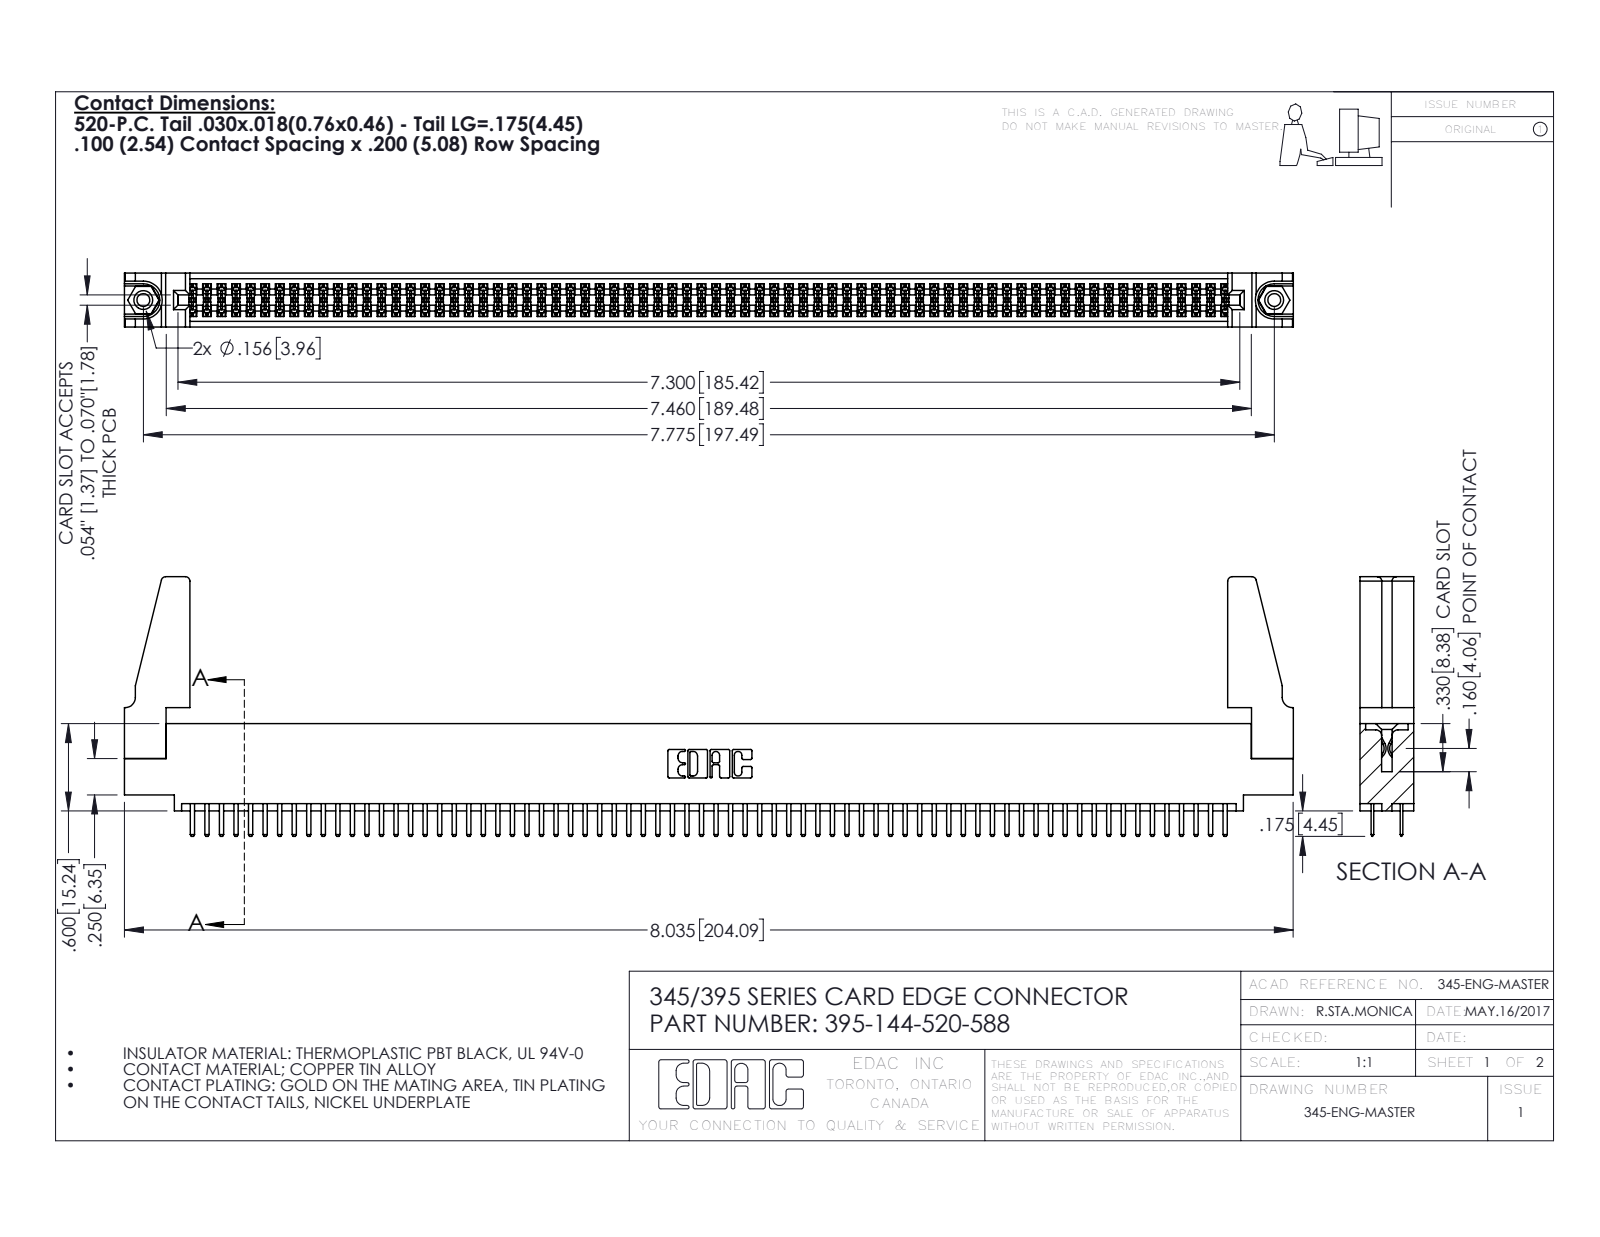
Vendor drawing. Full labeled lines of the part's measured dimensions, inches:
Part name (STEP PRODUCT): 345 Part_0.110 Offset - 0.156 Dia-TH; 345-292-001_345-293-120; 395-144-520-588; 345-250-001_345-250-001-102 (+1 more)
STEP written by: SolidWorks 2016 (CONFIG_CONTROL_DESIGN)
Units: inches
Bodies: 149 solids, 8030 faces (5196 planar, 2818 cylindrical, 16 other)
Overall size (bounding box): 8.036 × 1.785 × 0.37
Volume: 1.417 in³ · Surface area: 51.43 in²
Round holes (diameter × count): ⌀0.089 ×2, ⌀0.125 ×2, ⌀0.156 ×2, ⌀0.064 ×1
Round bosses / shafts (diameter × count): ⌀0.155 ×2
Partial cylindrical surfaces — rounded edges, fillets, slot ends (radius × count): R0.006 ×216, R0.01 ×148, R0.01 ×22, R0.03 ×8, R0.007 ×6, R0.031 ×6, R0.026 ×3, R0.014 ×2
Main face-to-face distances: 0.072, 0.298, 0.37, 0.2, 0.098, 0.272, 0.025, 0.225, 0.022, 0.072
Hole centre spacings: 0.27, 7.539, 7.775
